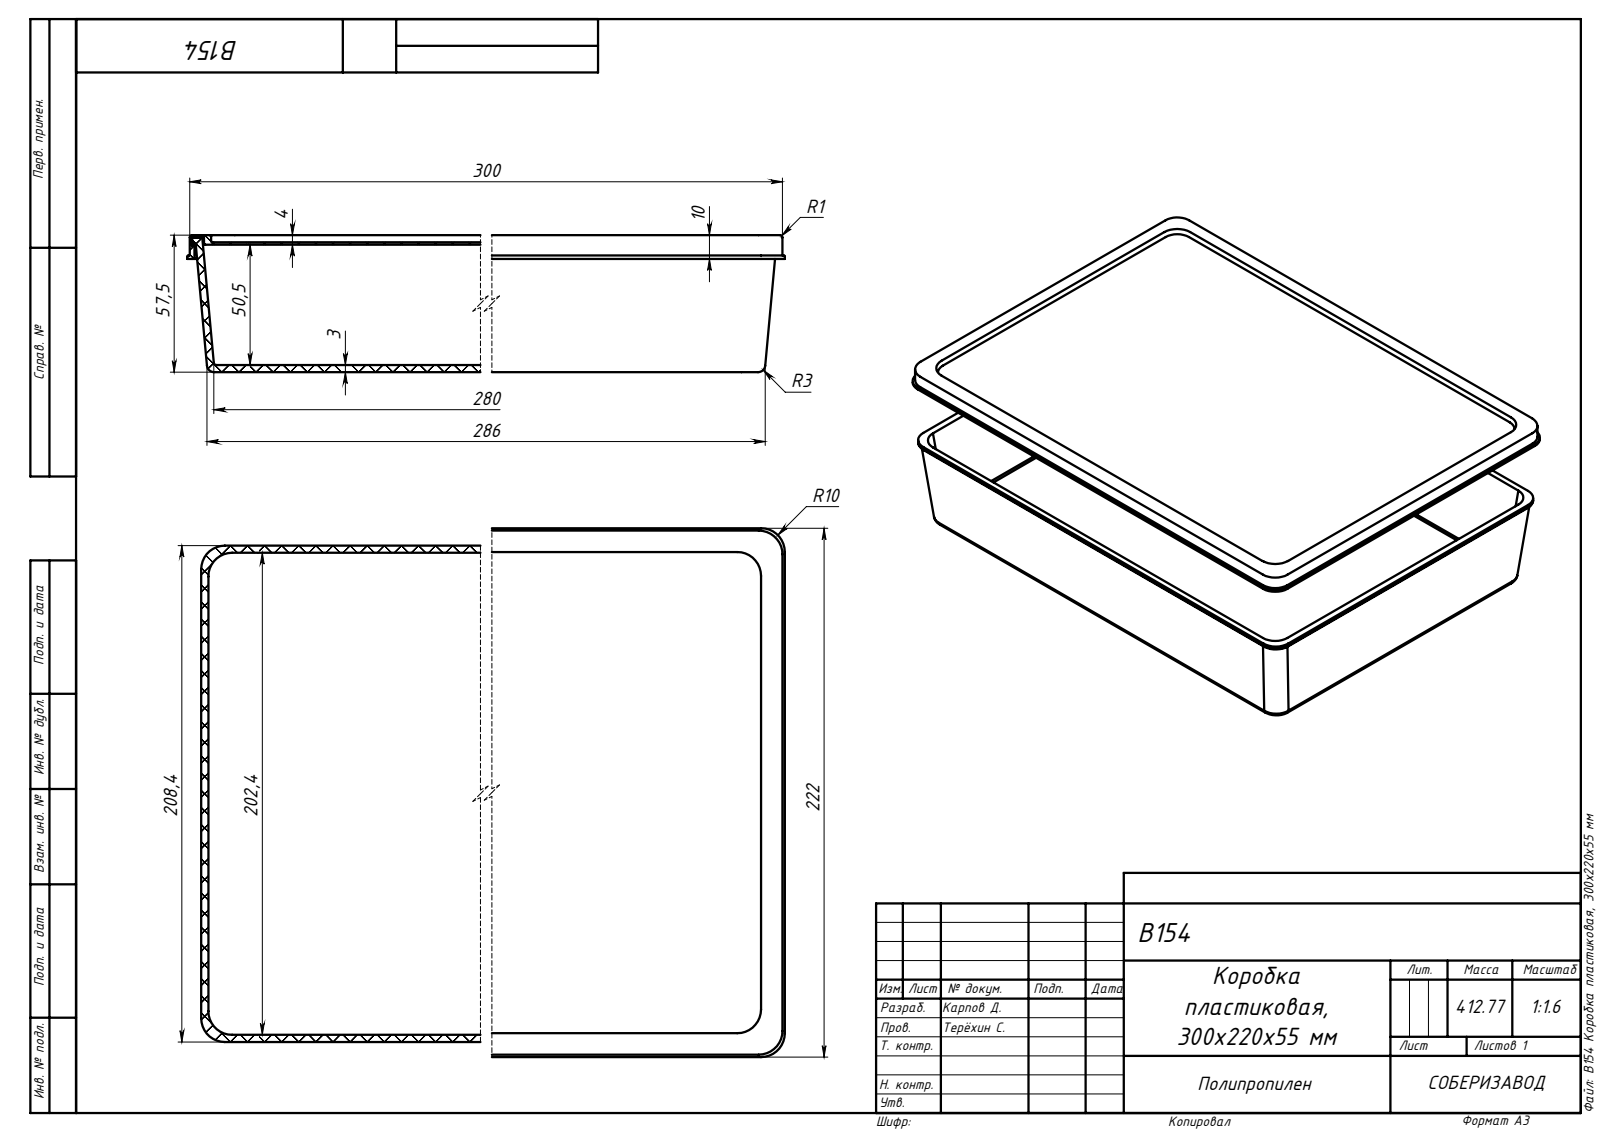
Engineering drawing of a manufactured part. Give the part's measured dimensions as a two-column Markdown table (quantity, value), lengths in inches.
| quantity | value |
| --- | --- |
| part name | B154 Емкость; B154 Коробка пластиковая, 300x220x55 мм; B154 Крышка |
| STEP written by | SolidWorks 2020 (AUTOMOTIVE_DESIGN) |
| units | inches |
| bodies | 2 solids, 266 faces (96 planar, 130 cylindrical, 40 other) |
| overall size | 11.89 × 8.74 × 2.264 |
| volume | 25.75 in³ |
| surface area | 593.1 in² |
| round bosses / shafts (diameter × count) | 0.315 × 1 |
| partial cylindrical surfaces (radius × count) | 0.004 × 52, 0.394 × 32, 0.02 × 16, 0.039 × 13, 0.118 × 4 |
| main face-to-face distances | 0.118, 0.039, 2.106, 2.146, 1.988, 2.028, 0.079, 2.224, 0.157, 2.264 |
